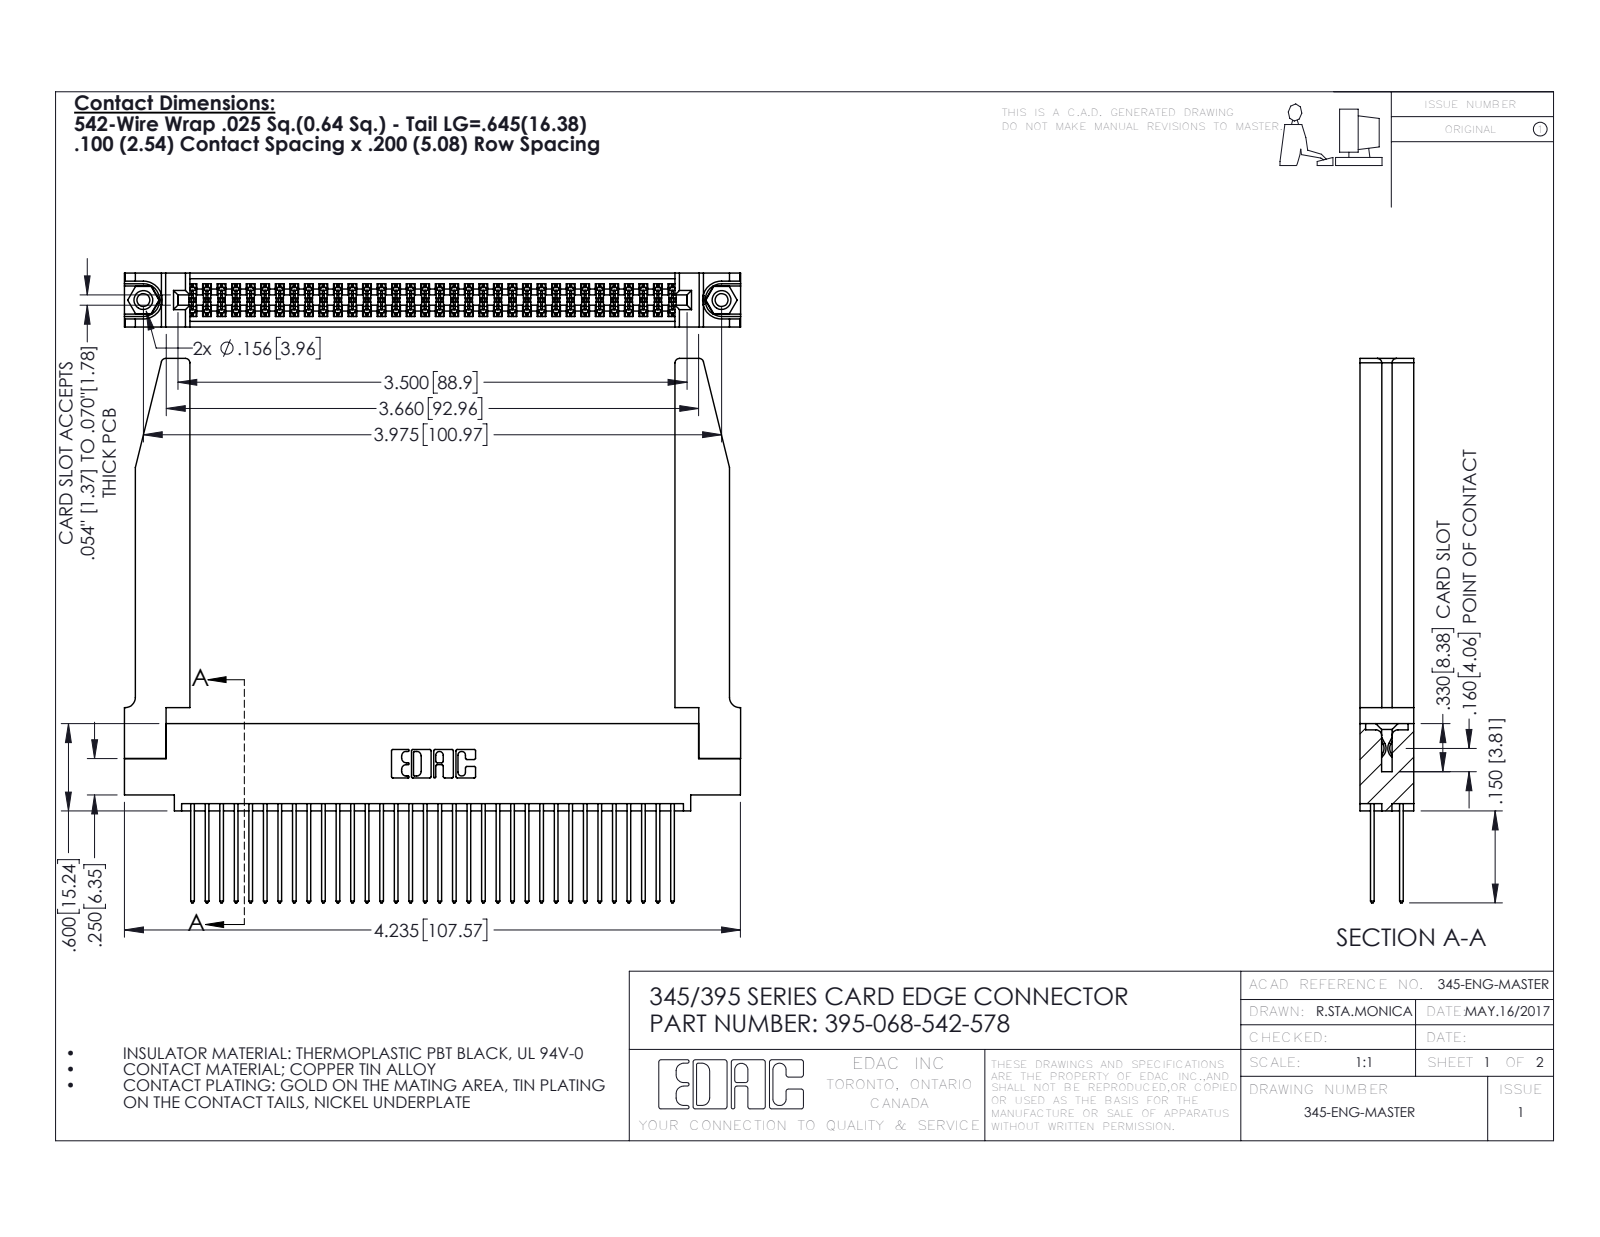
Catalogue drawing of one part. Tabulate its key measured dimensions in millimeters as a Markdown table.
| quantity | value |
| --- | --- |
| part name | 345-220-078_345-220-078; 345 Part_0.110 Offset - 0.156 Dia-TH; 395-068-542-578; 345-292-001_345-293-142 (+1 more) |
| STEP written by | SolidWorks 2016 (CONFIG_CONTROL_DESIGN) |
| units | millimeters |
| bodies | 73 solids, 3764 faces (2470 planar, 1242 cylindrical, 52 other) |
| overall size | 107.6 × 95 × 9.4 |
| volume | 18 390 mm³ |
| surface area | 23 950 mm² |
| round holes (diameter × count) | 2.3 × 2, 3.2 × 2, 4 × 2, 1.6 × 1 |
| round bosses / shafts (diameter × count) | 3.9 × 2 |
| partial cylindrical surfaces (radius × count) | 0.2 × 102, 0.3 × 68, 0.3 × 22, 0.8 × 8, 0.2 × 6, 0.8 × 6, 0.7 × 3, 0.4 × 2 |
| main face-to-face distances | 1.8, 7.6, 9.4, 5.1, 2.5, 6.9, 0.6, 5.7, 4.4, 3.8 |
| hole center spacings | 6.9, 95, 101 |
